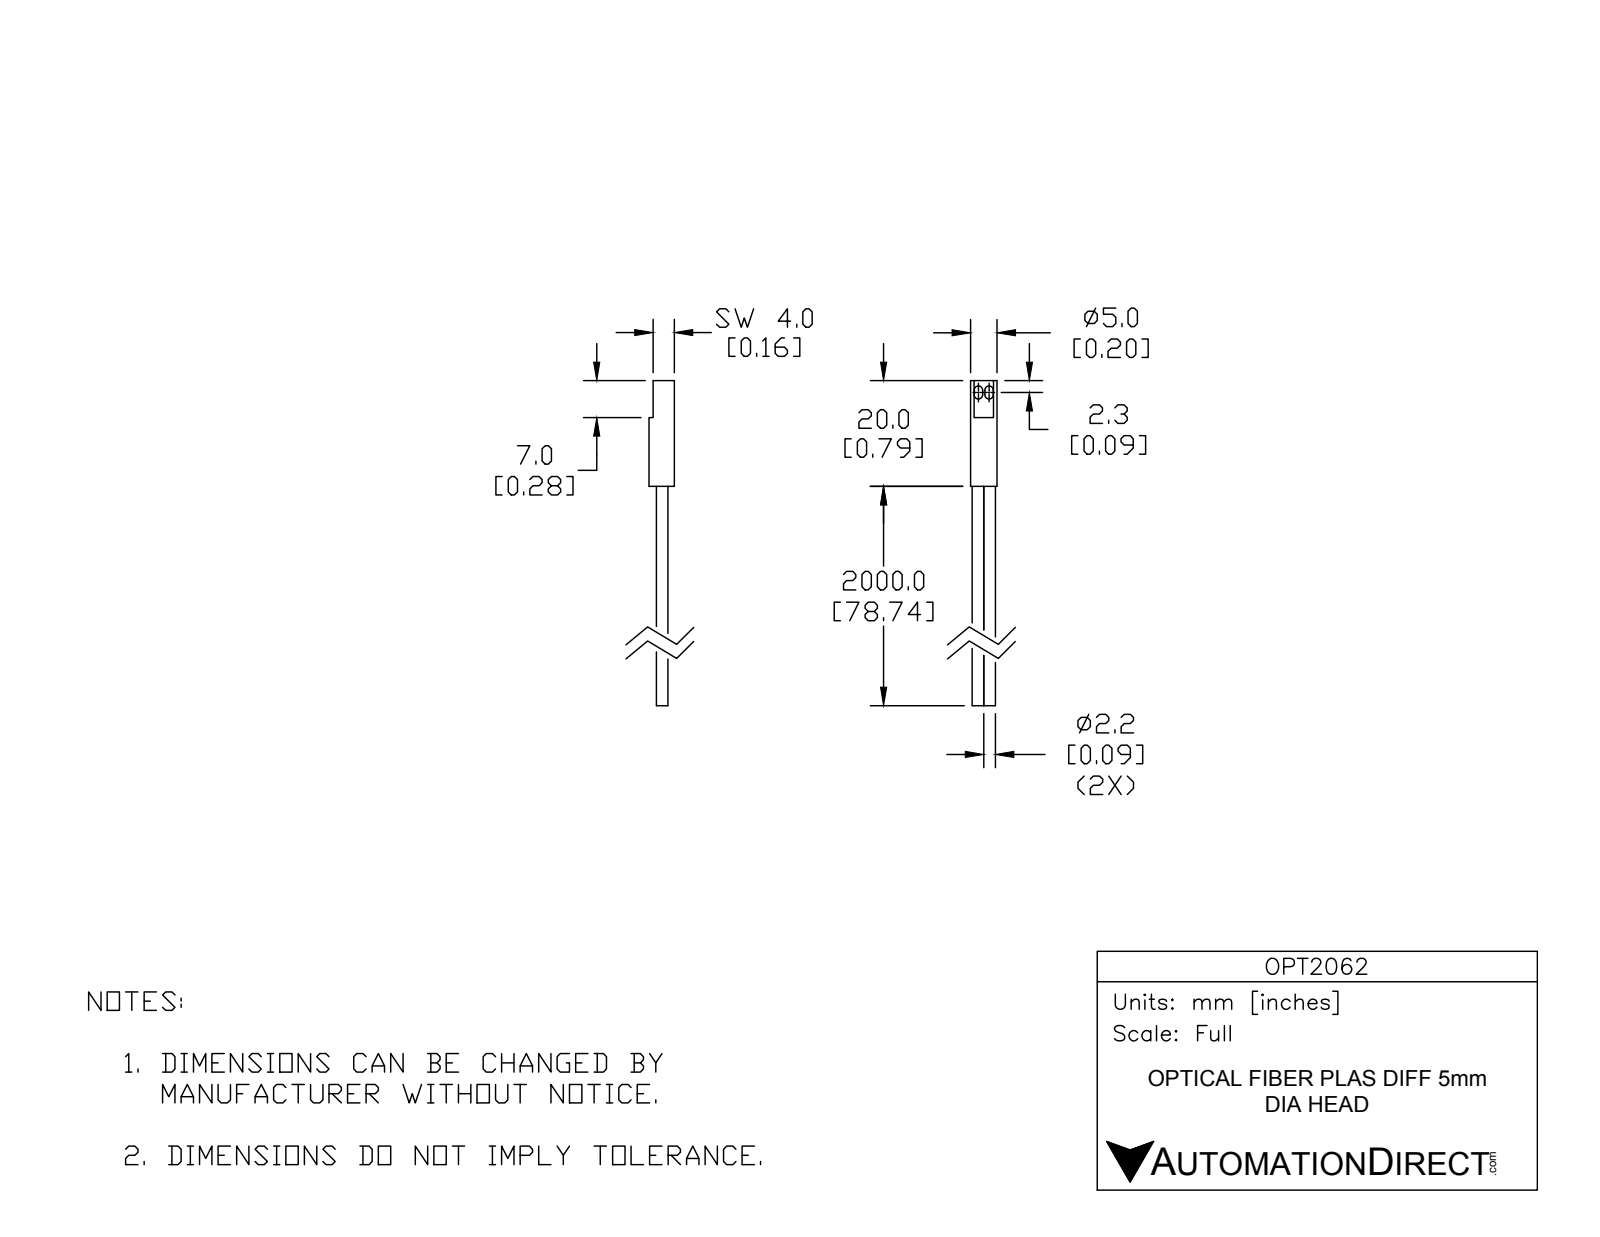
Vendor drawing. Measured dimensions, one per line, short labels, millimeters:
name: OPT2062
written by: SolidWorks 2014 (AUTOMOTIVE_DESIGN)
unit: mm
bodies: 1 solid, 62 faces (22 planar, 38 cylindrical, 2 other)
size: 61.5 × 5 × 4.8
volume: 660 mm³; area: 1 041 mm²
holes: 1× ⌀4.3
bosses: 2× ⌀2.2, 1× ⌀5
rounds: 4× R0.8, 2× R0.5, 2× R0.6, 1× R1.2
face distances: 4, 20, 41.5, 61.5, 49.1, 7.6, 12.4, 50, 8.5, 0.9
